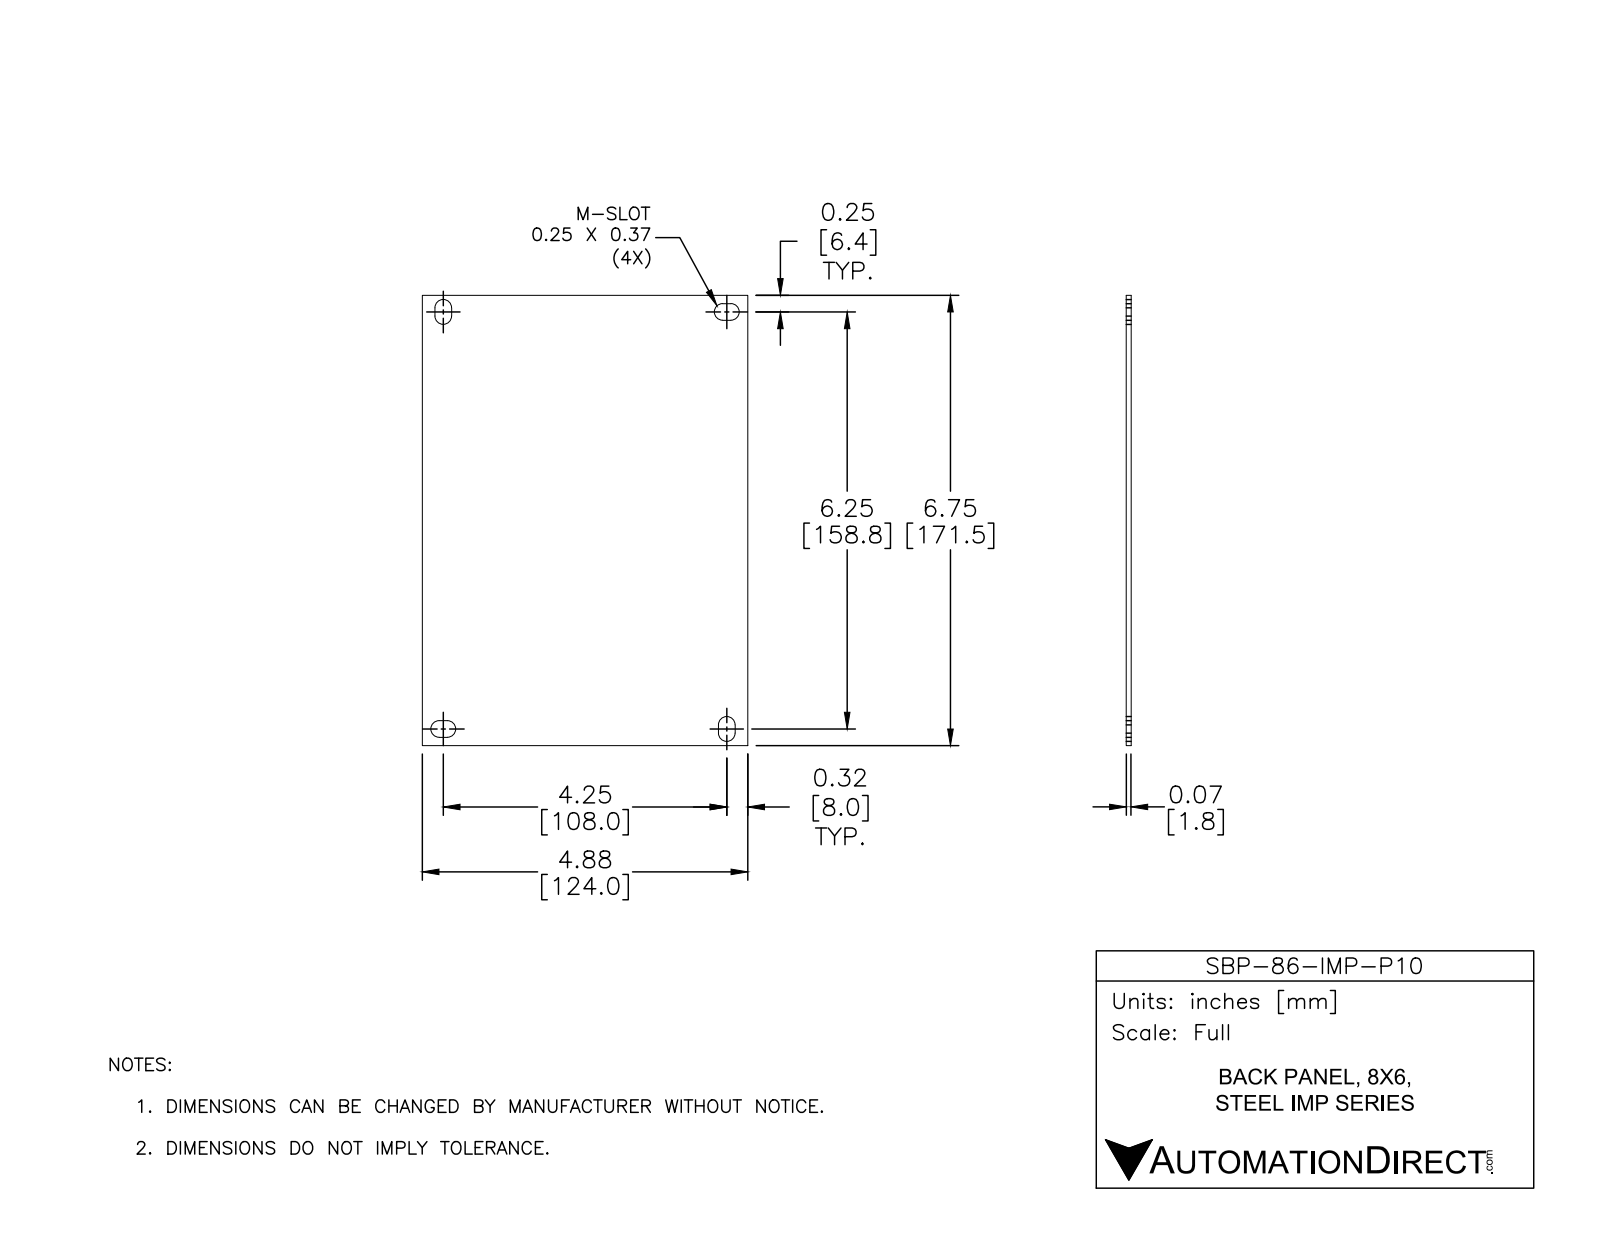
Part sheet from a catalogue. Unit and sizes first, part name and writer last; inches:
Units: inches
Overall size (bounding box): 6.75 × 4.88 × 0.064
Partial cylindrical surfaces — rounded edges, fillets, slot ends (radius × count): R0.125 ×8
Main face-to-face distances: 0.064, 4.88, 6.75, 0.25, 0.125, 6.625, 4.25, 0.375, 6.375, 6.375
Volume: 2.091 in³ · Surface area: 67 in²
Bodies: 1 solid, 24 faces (14 planar, 10 cylindrical, 0 other)
Part name (STEP PRODUCT): SBP-86-IMP-P604
STEP written by: SolidWorks 2016 (AUTOMOTIVE_DESIGN)
